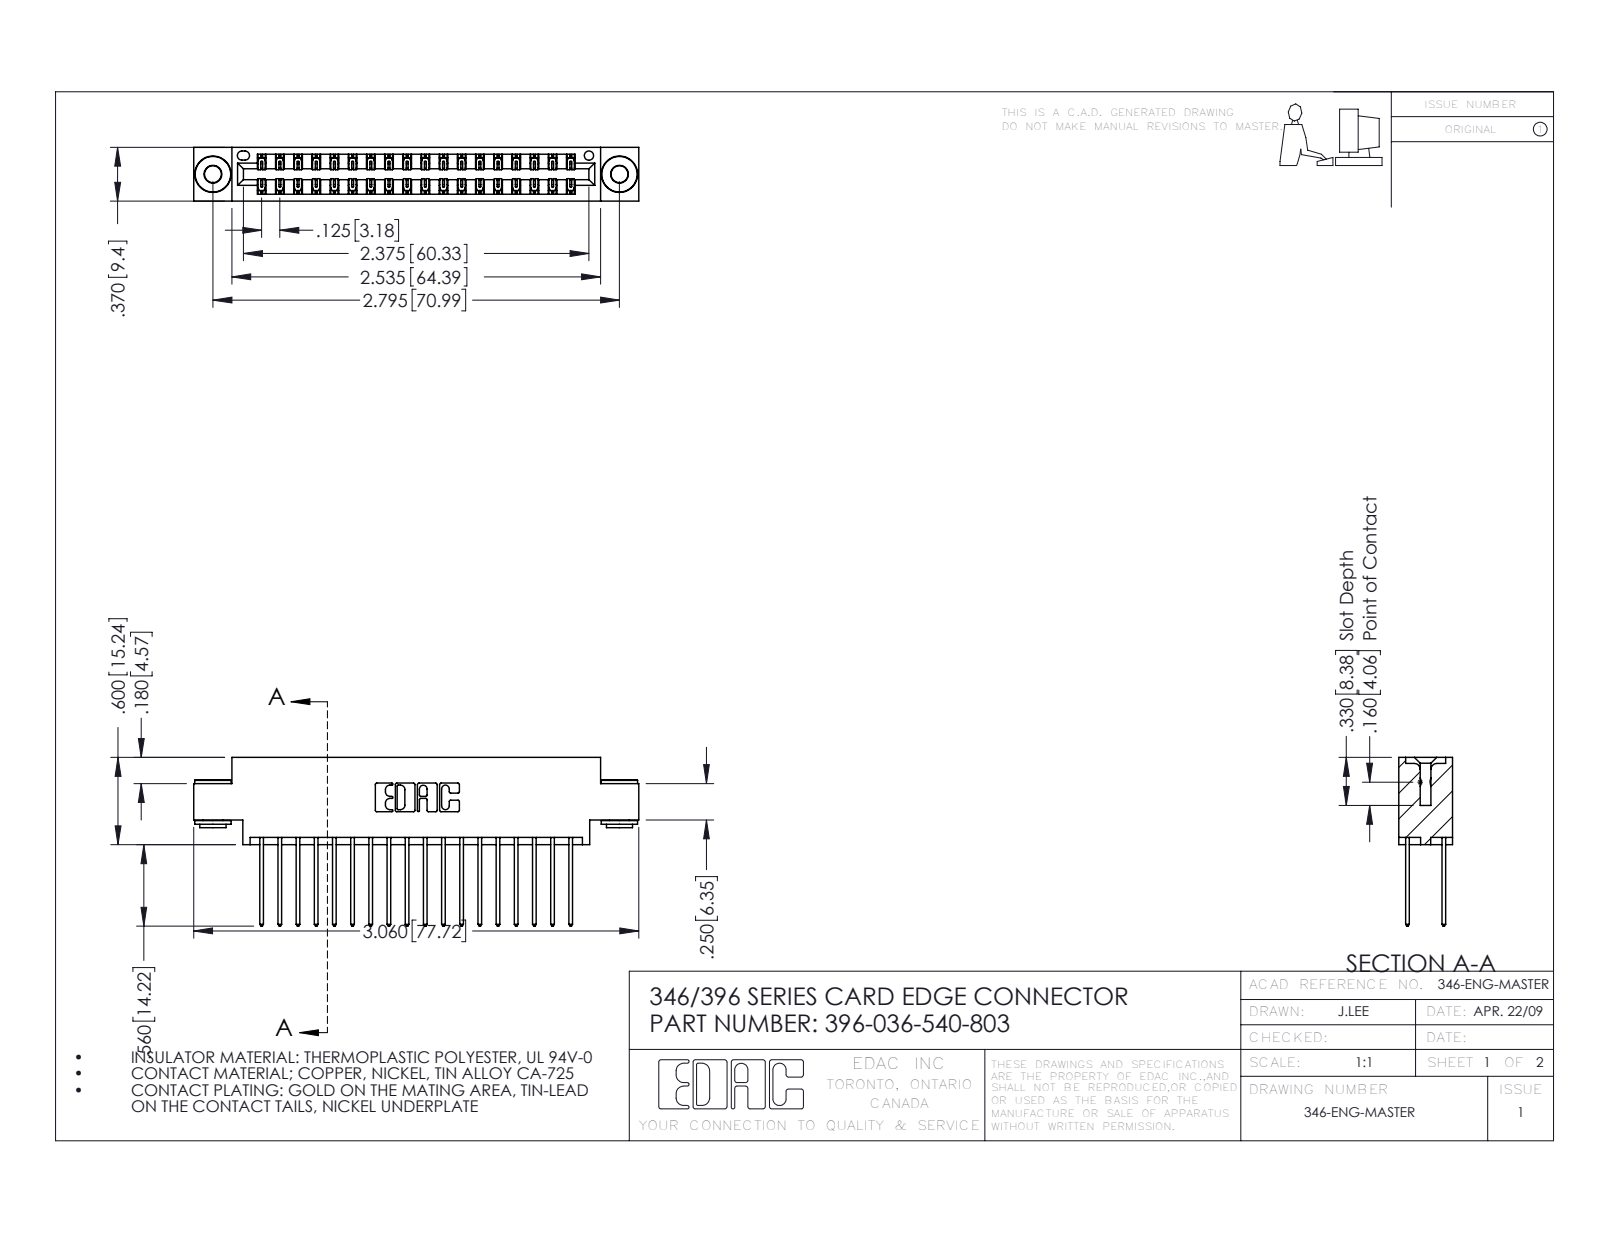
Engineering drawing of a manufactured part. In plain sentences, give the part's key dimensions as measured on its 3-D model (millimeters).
The part is named "345-250-002_345-250-002-102; 346 Part_0.170 Offset - 0.156 Dia-TH; 396-036-540-803; 345-292-001_345-293-140". Its 3-D file was written by "SolidWorks 2016 (CONFIG_CONTROL_DESIGN)". It is 39 solids with 2036 faces: 1350 planar, 678 cylindrical and 8 other. Overall it measures 77.7 by 29.5 by 9.4 millimeters. Its volume is 7 390 cubic millimeters and its surface area 10 830 square millimeters. Round holes: 2 of diameter 2.9, 2 of diameter 4, 1 of diameter 1.6. Round bosses or shafts: 2 of diameter 6.4, 2 of diameter 4.6, 2 of diameter 3.5. Partial cylindrical surfaces (rounded edges, fillets, slot ends): 54 of radius 0.2, 36 of radius 0.3, 22 of radius 0.3, 6 of radius 0.2, 6 of radius 0.8, 3 of radius 0.7, 2 of radius 0.4, 2 of radius 0.6. The main face-to-face distances are 1.2, 8.2, 6.4, 9.4, 0.6, 1.8, 7.6, 7, 3.8, 5.6. The hole center spacings are 6.2, 65.7, 71.
